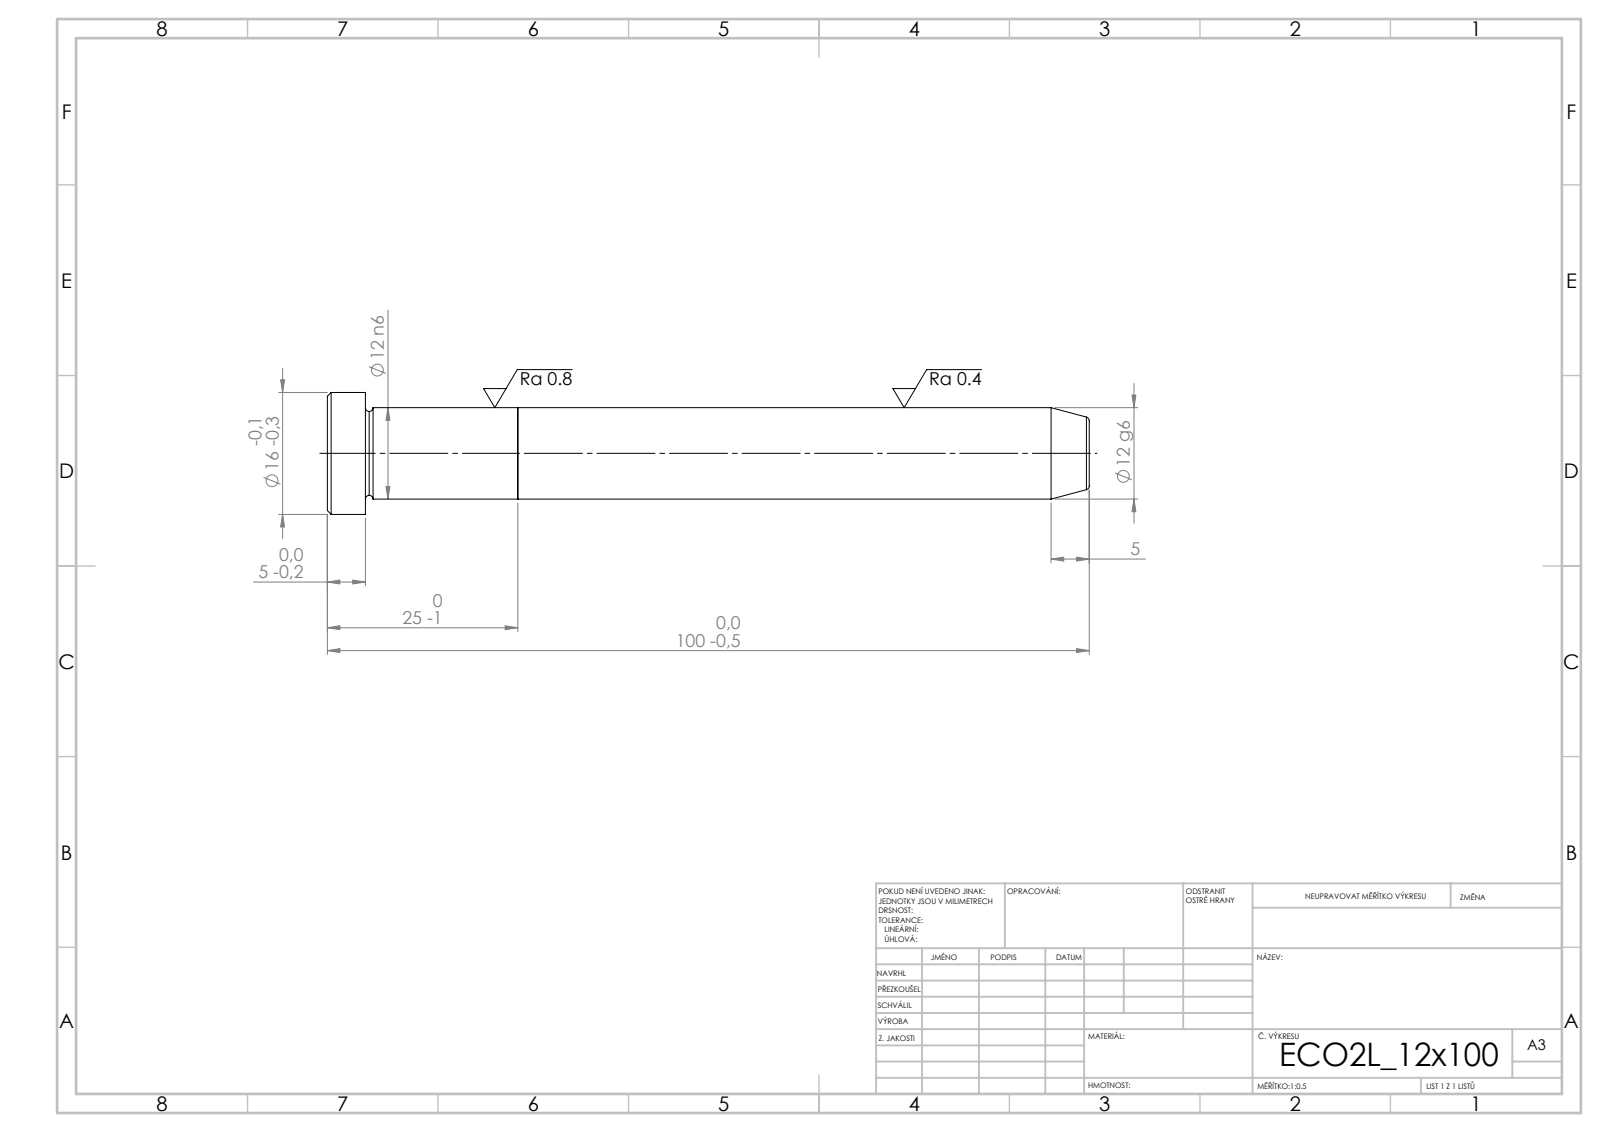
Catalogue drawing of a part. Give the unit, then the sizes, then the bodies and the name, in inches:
Units: inches
Overall size (bounding box): 3.937 × 0.63 × 0.63
Round bosses / shafts (diameter × count): ⌀0.63 ×1, ⌀0.472 ×1
Main face-to-face distances: 0.984, 0.787, 0.197, 2.953, 3.74, 3.937
Volume: 0.709 in³ · Surface area: 6.822 in²
Bodies: 2 solids, 21 faces (5 planar, 6 cylindrical, 10 other)
STEP written by: SolidWorks 2019 (CONFIG_CONTROL_DESIGN)
